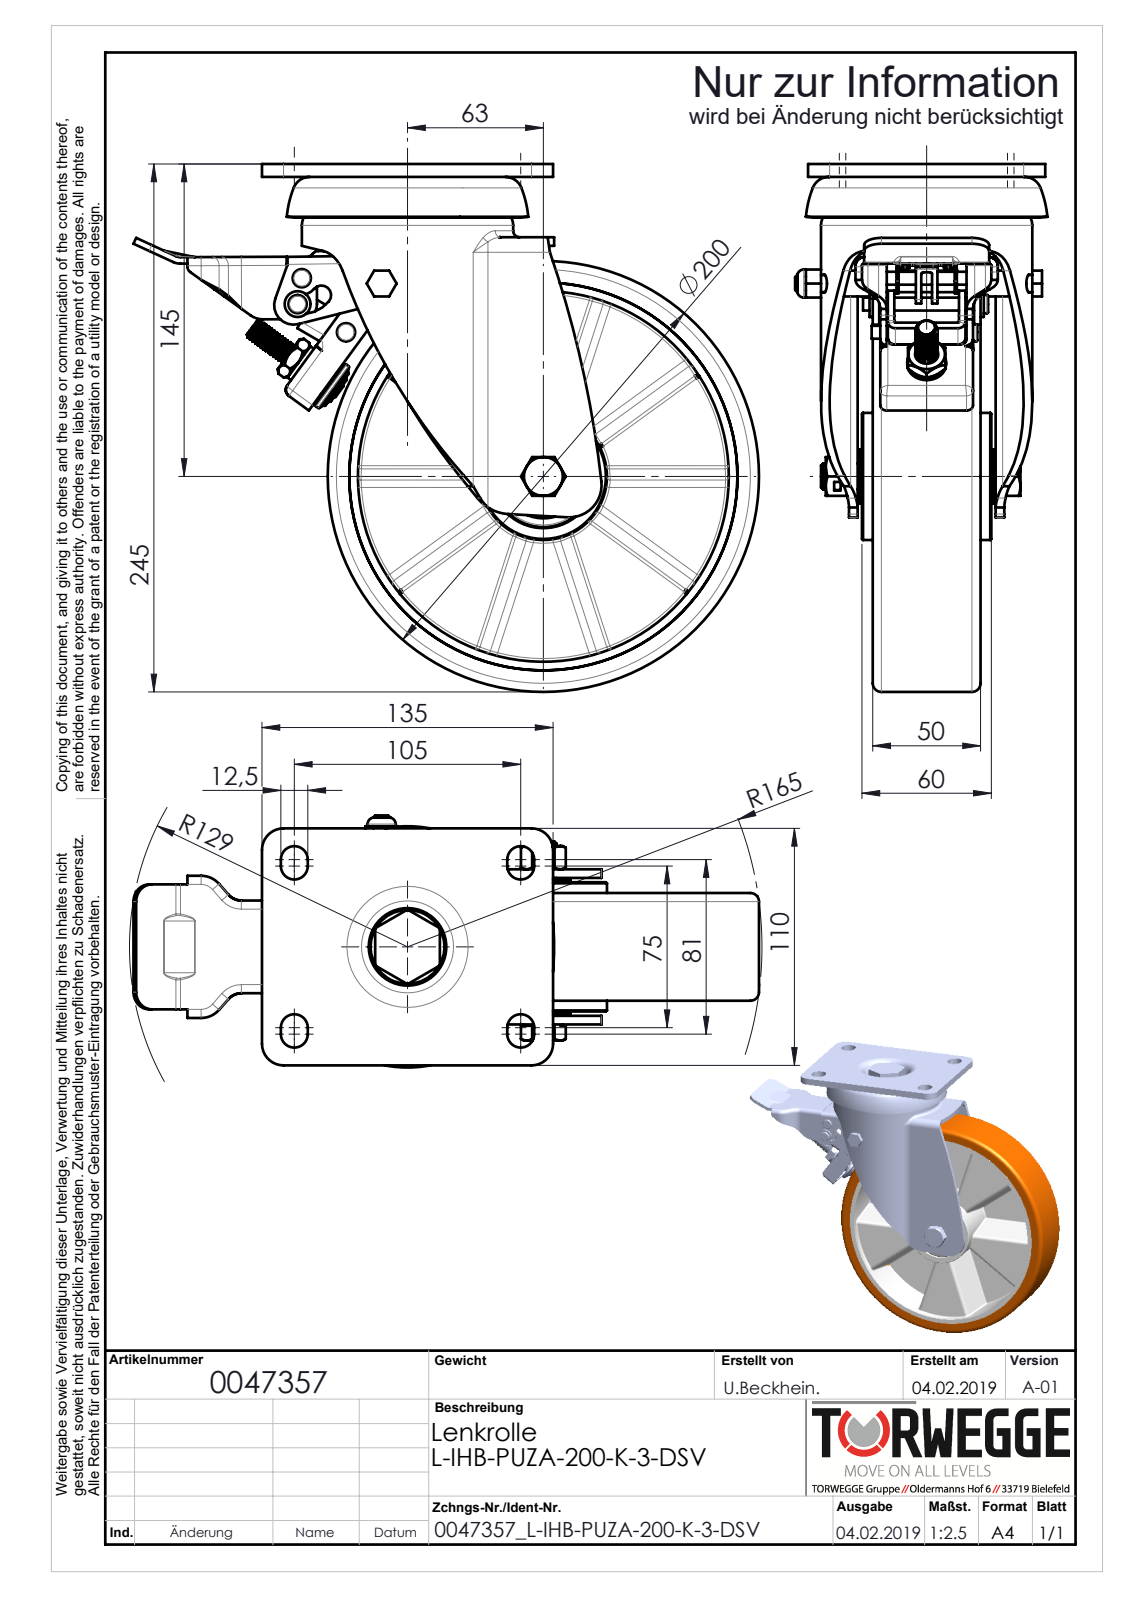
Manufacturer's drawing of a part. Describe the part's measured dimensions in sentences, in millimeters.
The part is named "0047357_L-IHB-PUZA-200-K-3-DSV_(A-01)". Its 3-D file was written by "SolidWorks 2018 (AUTOMOTIVE_DESIGN)". It is 0 solids with 1435 faces: 401 planar, 495 cylindrical and 539 other. Overall it measures 290.11 by 245 by 117 millimeters. Round holes: 3 of diameter 4, 3 of diameter 6.5, 2 of diameter 5, 2 of diameter 7.8, 2 of diameter 12, 2 of diameter 20.5, 1 of diameter 8.5, 1 of diameter 10, 1 of diameter 10.2, 1 of diameter 10.5, 1 of diameter 12.2, 1 of diameter 12.5. Round bosses or shafts: 3 of diameter 8.5, 3 of diameter 6, 2 of diameter 20, 2 of diameter 18, 1 of diameter 200, 1 of diameter 98, 1 of diameter 83, 1 of diameter 59. Partial cylindrical surfaces (rounded edges, fillets, slot ends): 40 of radius 1, 28 of radius 3.5, 12 of radius 1.5, 11 of radius 0.5, 11 of radius 4, 10 of radius 6.25, 8 of radius 2, 8 of radius 3. The main face-to-face distances are 6, 4, 10.5, 17.5, 33.5, 44, 4.5, 11, 55, 50.5. The hole center spacings are 10, 12.17, 25.99, 28, 32.4, 37.12, 40.14, 113.37.
